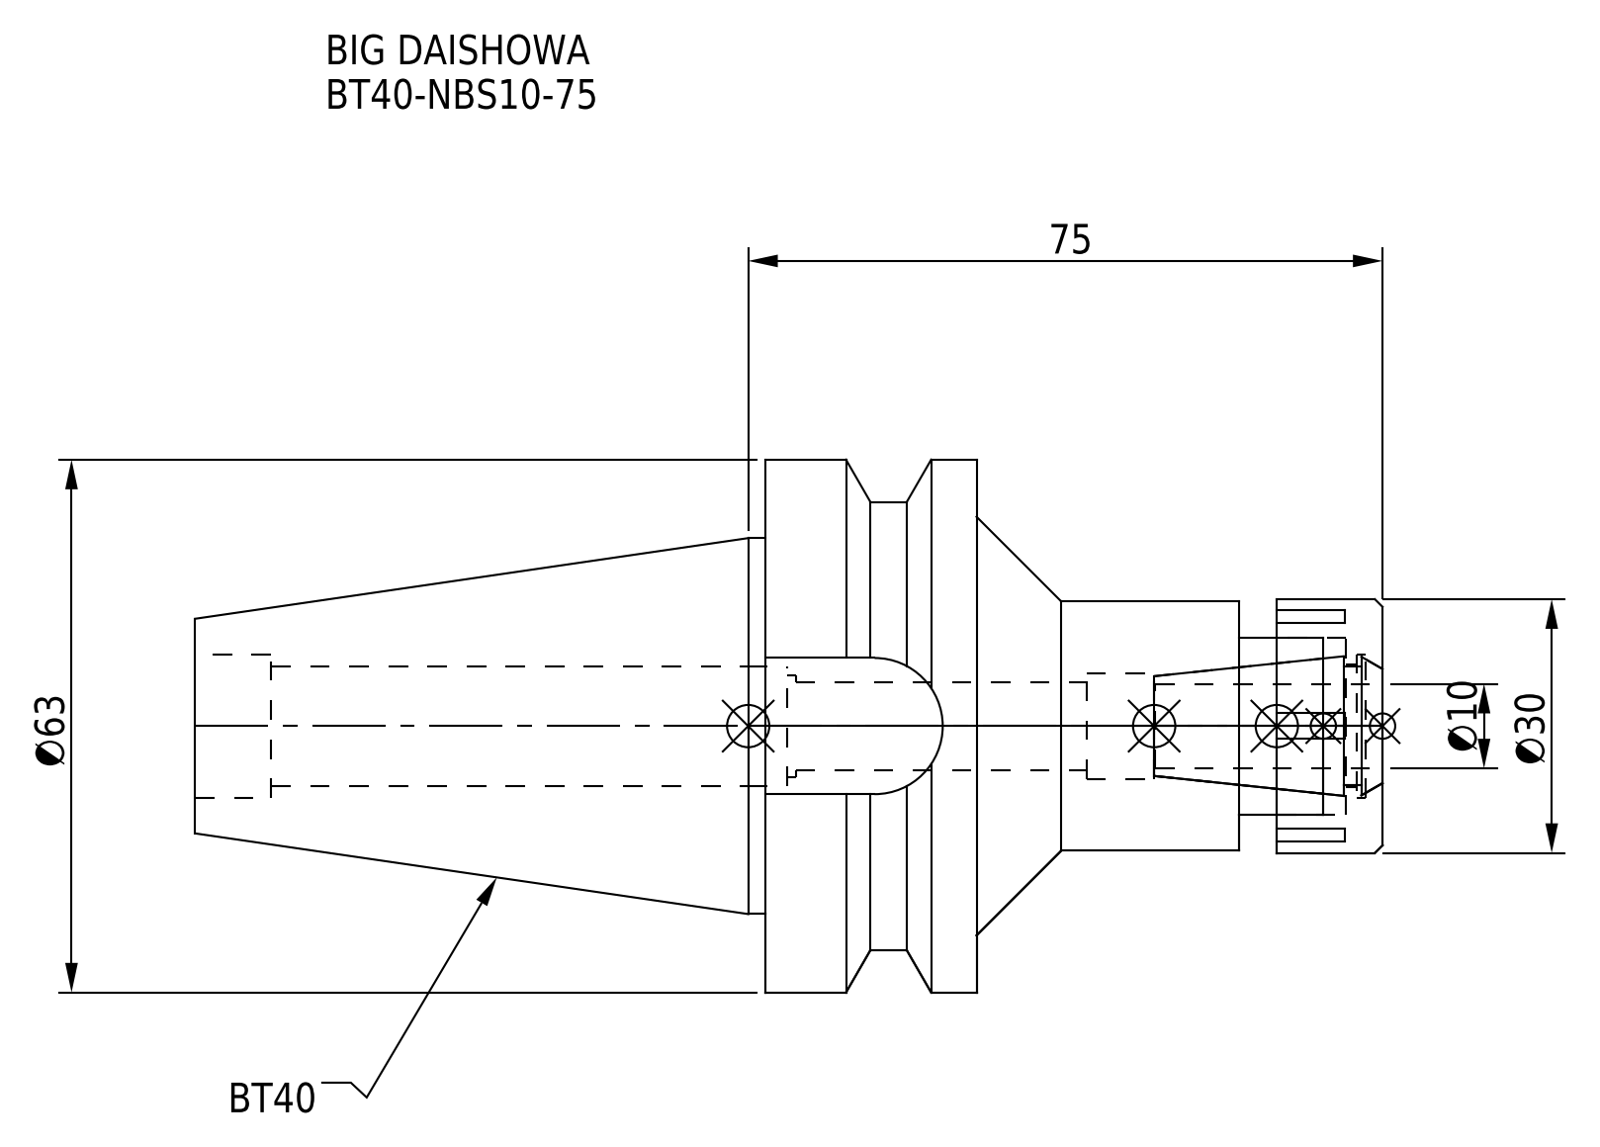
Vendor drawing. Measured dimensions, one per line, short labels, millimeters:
name: BT40-NBS10-75_1.stp; BT40-NBS10-75-FreeParts; DXF_TEMP_ASSY_ASM_4_ASM.stp; NBN10_1.stp (+3 more)
written by: SolidWorks 2019 (CONFIG_CONTROL_DESIGN)
unit: mm
bodies: 2 solids, 93 faces (45 planar, 34 cylindrical, 14 other)
size: 140.4 × 63 × 63
volume: 150 742 mm³; area: 30 433 mm²
holes: 1× ⌀10.4, 1× ⌀12, 1× ⌀12.5, 1× ⌀14.2, 1× ⌀14.5, 1× ⌀17, 1× ⌀21
bosses: 1× ⌀63, 1× ⌀53, 1× ⌀44.45, 1× ⌀30, 1× ⌀29.5
rounds: 1× R8.05
face distances: 25, 48, 73, 35.5, 45, 4.5, 12.5, 67.4, 17, 31
